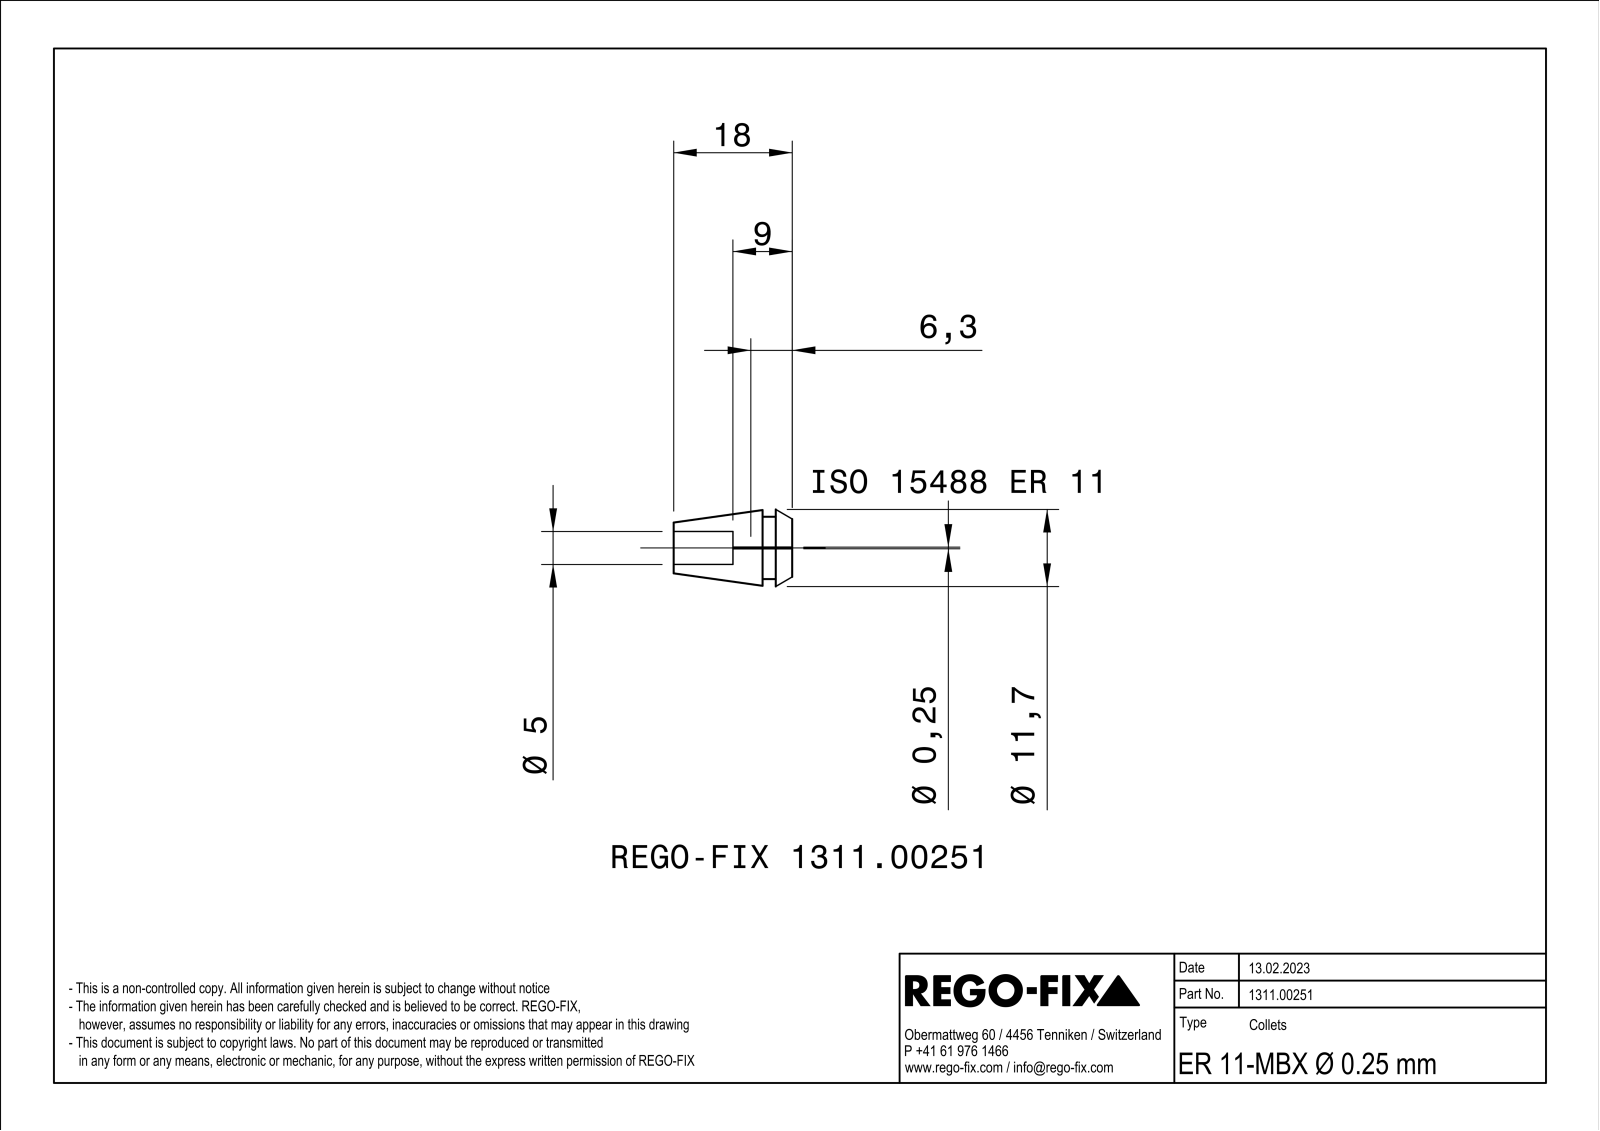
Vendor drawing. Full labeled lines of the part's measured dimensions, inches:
Part name (STEP PRODUCT): NOCUT
STEP written by: SIEMENS PLM Software Solid Edge ST10 (AUTOMOTIVE_DESIGN)
Units: inches
Bodies: 1 solid, 91 faces (26 planar, 19 cylindrical, 46 other)
Overall size (bounding box): 0.709 × 0.449 × 0.448
Volume: 0.061 in³ · Surface area: 1.955 in²
Round holes (diameter × count): ⌀0.059 ×3, ⌀0.197 ×1
Round bosses / shafts (diameter × count): ⌀0.374 ×1
Partial cylindrical surfaces — rounded edges, fillets, slot ends (radius × count): R0.984 ×3, R0.005 ×1
Main face-to-face distances: 0.031, 0.013, 0.018, 0.177, 0.354, 0.709, 0.531, 0.098, 0.079, 0.61
Hole centre spacings: 0.067, 0.116
